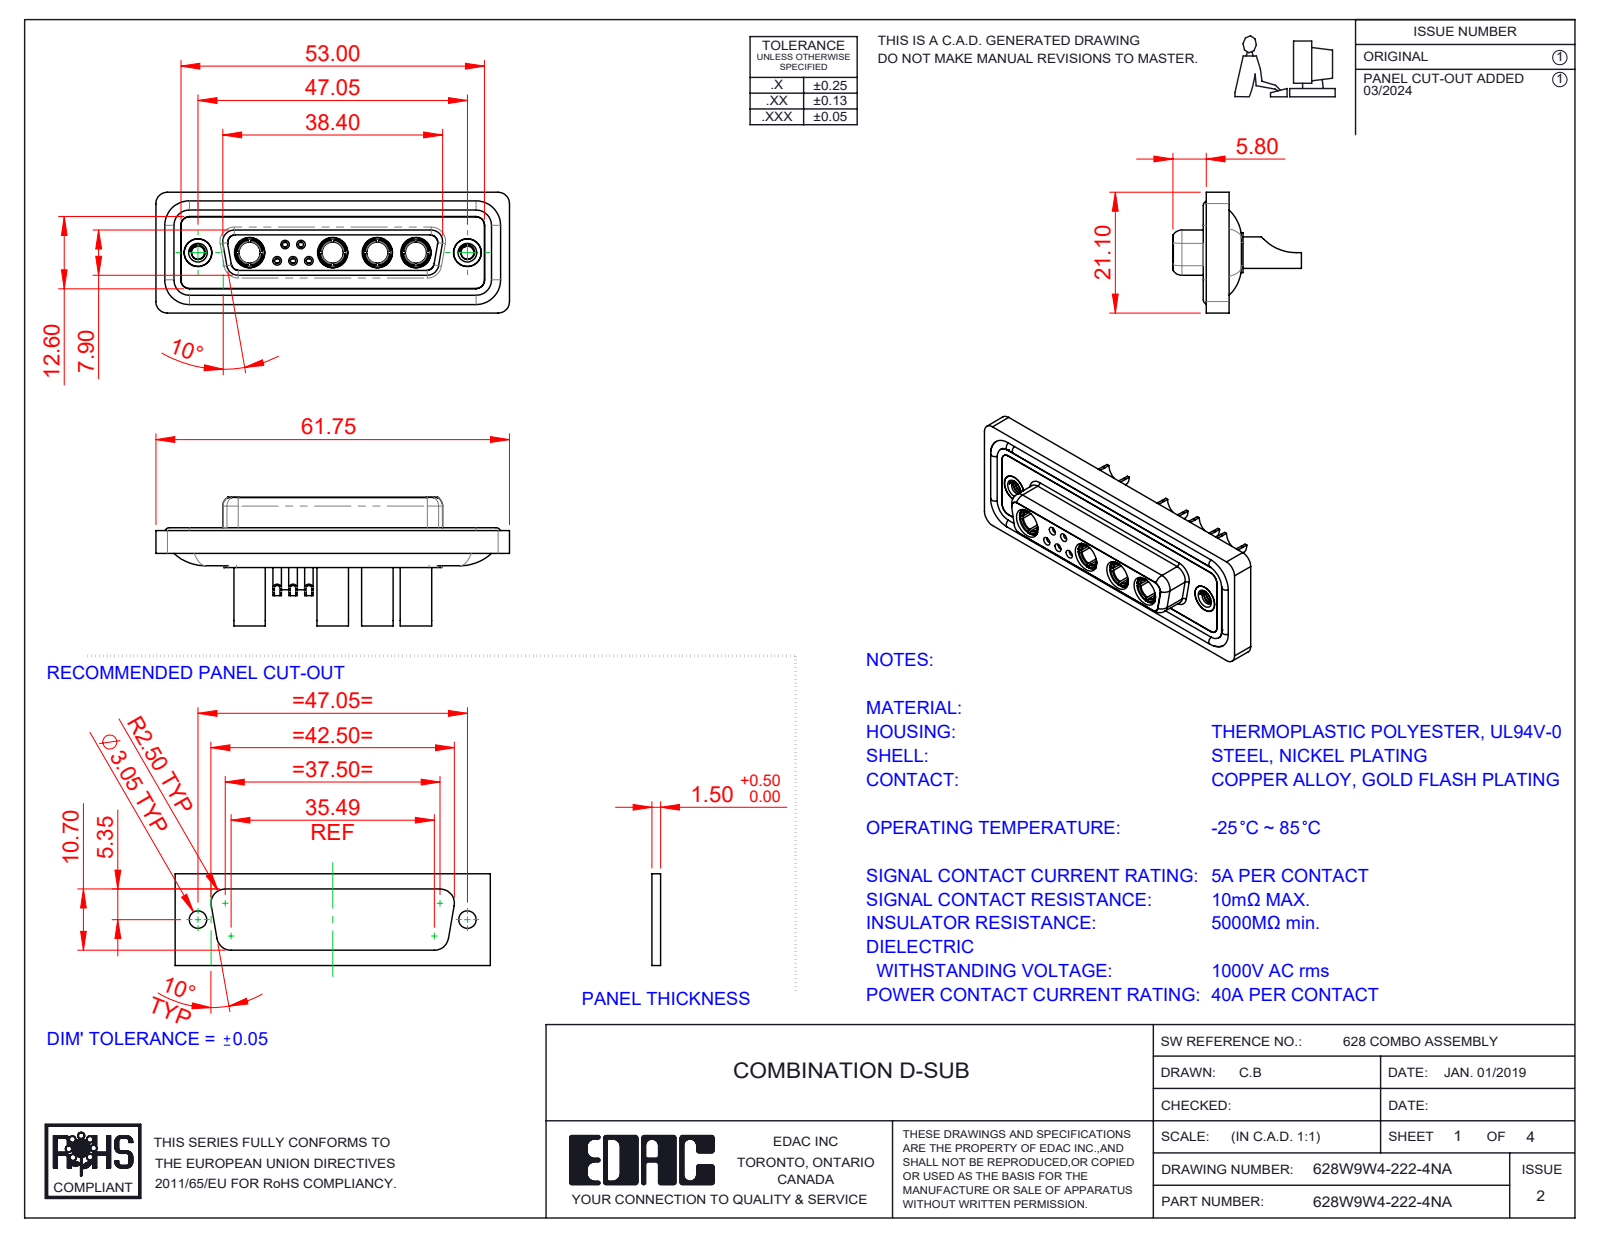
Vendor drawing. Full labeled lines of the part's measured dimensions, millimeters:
Part name (STEP PRODUCT): 628W9W4-222-4NA; Power Socket_40A SC; 628Combo Contact Row 1_22; 628Combo Shell Rear_25 Contacts (+5 more)
STEP written by: SolidWorks 2023 (CONFIG_CONTROL_DESIGN)
Units: millimetres
Bodies: 20 solids, 967 faces (314 planar, 391 cylindrical, 262 other)
Overall size (bounding box): 61.75 × 22.45 × 21.1
Volume: 8 396 mm³ · Surface area: 14 174 mm²
Round holes (diameter × count): ⌀4.85 ×6, ⌀0.9 ×5, ⌀1 ×5, ⌀1.1 ×5, ⌀1.5 ×5, ⌀2 ×5, ⌀3.7 ×4, ⌀4.6 ×4, ⌀5.3 ×4, ⌀1.6 ×3, ⌀1.7 ×2, ⌀2.26 ×2
Round bosses / shafts (diameter × count): ⌀1.6 ×6, ⌀2.2 ×5, ⌀5.5 ×4, ⌀5.2 ×4, ⌀4.96 ×4, ⌀4.75 ×4, ⌀3.75 ×4, ⌀4.95 ×2
Partial cylindrical surfaces — rounded edges, fillets, slot ends (radius × count): R1.5 ×22, R2 ×18, R1.35 ×8, R1.6 ×8, R1 ×6, R0.25 ×4, R0.5 ×4, R0.6 ×4
Main face-to-face distances: 0.4, 7.45, 1.8, 5.65, 0.5, 7.05, 6.6, 1.6, 1.1, 2.9
Hole centre spacings: 3.16, 2.77, 5.03, 2.76, 4.4, 5.02, 5.54, 5.73
